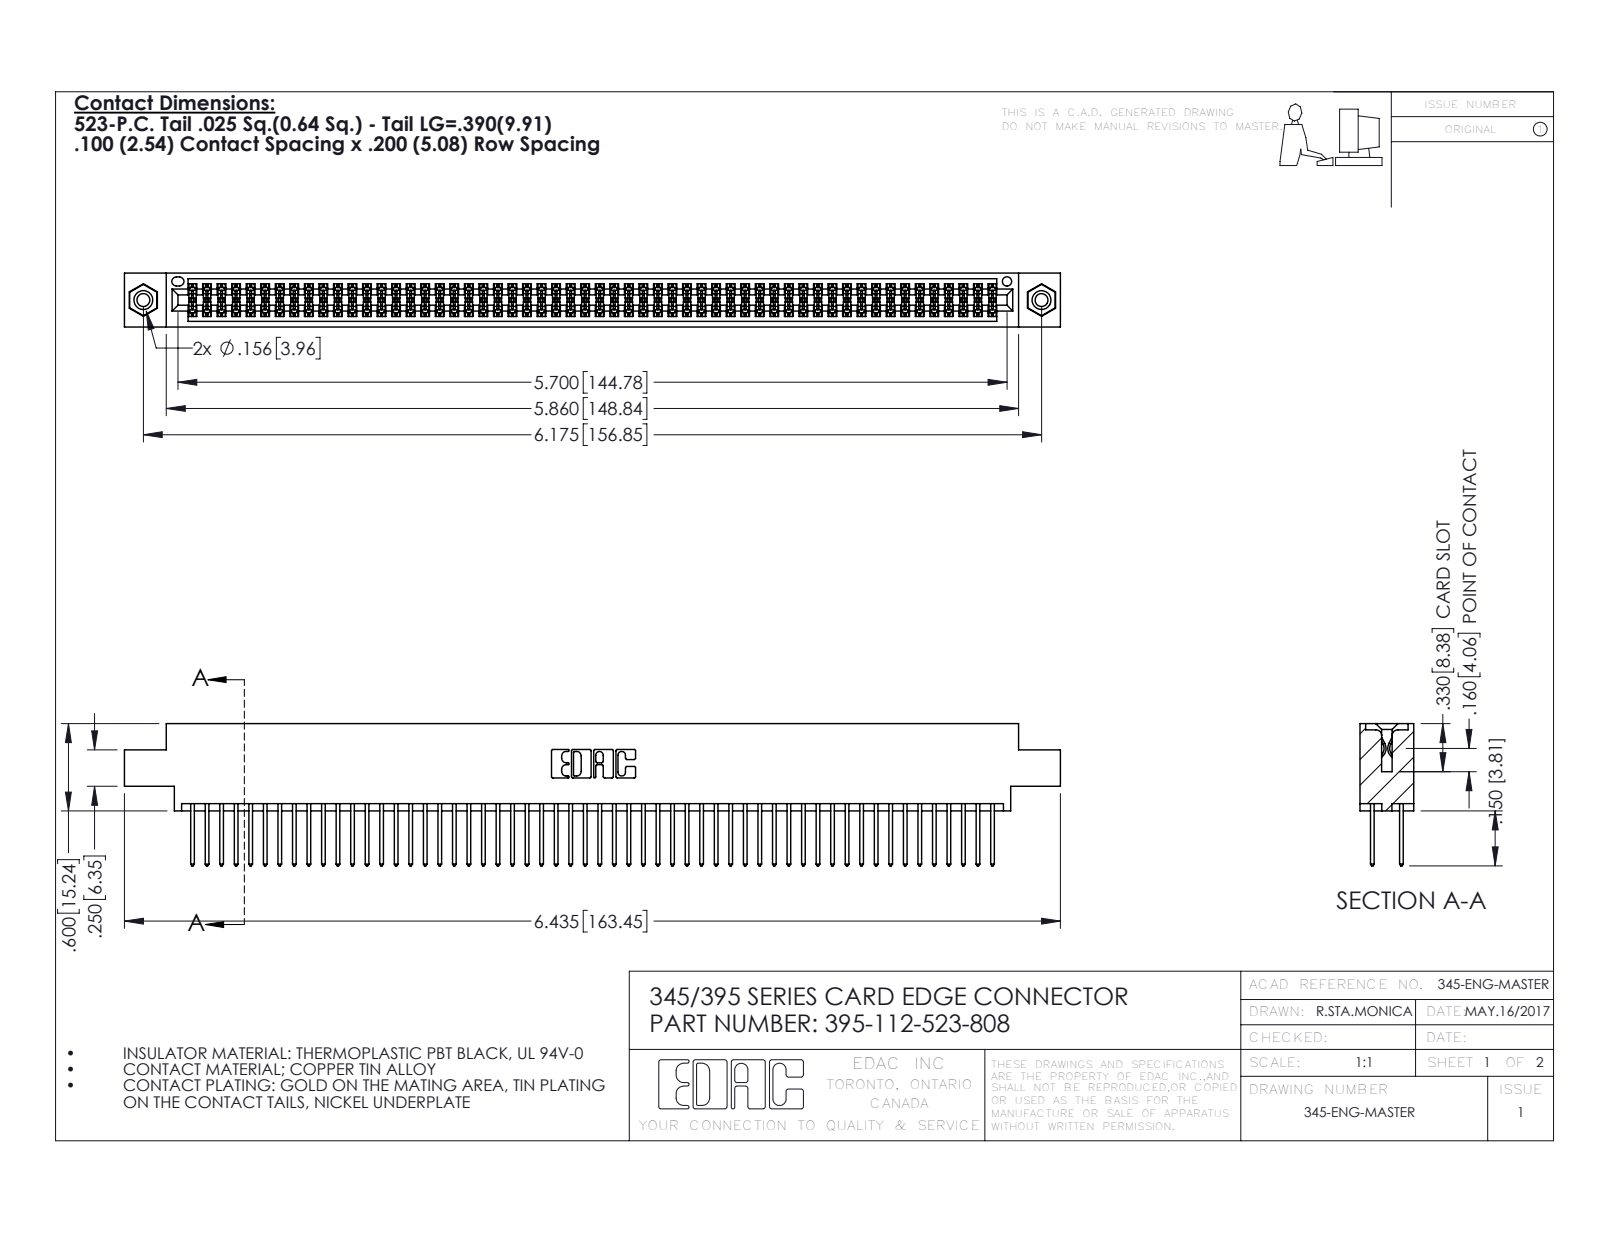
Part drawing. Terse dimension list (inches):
name: 345 Part_0.170 Offset - 0.156 Dia-TI; 395-112-523-808; 345-250-001_345-250-003-102; 345-292-001_345-293-123
written by: SolidWorks 2016 (CONFIG_CONTROL_DESIGN)
unit: in
bodies: 115 solids, 5790 faces (3812 planar, 1962 cylindrical, 16 other)
size: 6.435 × 0.977 × 0.37
volume: 0.984 in³; area: 39.19 in²
holes: 2× ⌀0.089, 2× ⌀0.125, 2× ⌀0.156, 1× ⌀0.064
bosses: 2× ⌀0.155
rounds: 168× R0.006, 112× R0.01, 22× R0.01, 6× R0.007, 6× R0.031, 3× R0.026, 2× R0.014, 2× R0.019
face distances: 0.072, 0.298, 0.2, 0.098, 0.272, 0.025, 0.37, 0.225, 0.175, 0.149
hole spacings: 0.27, 5.939, 6.175
